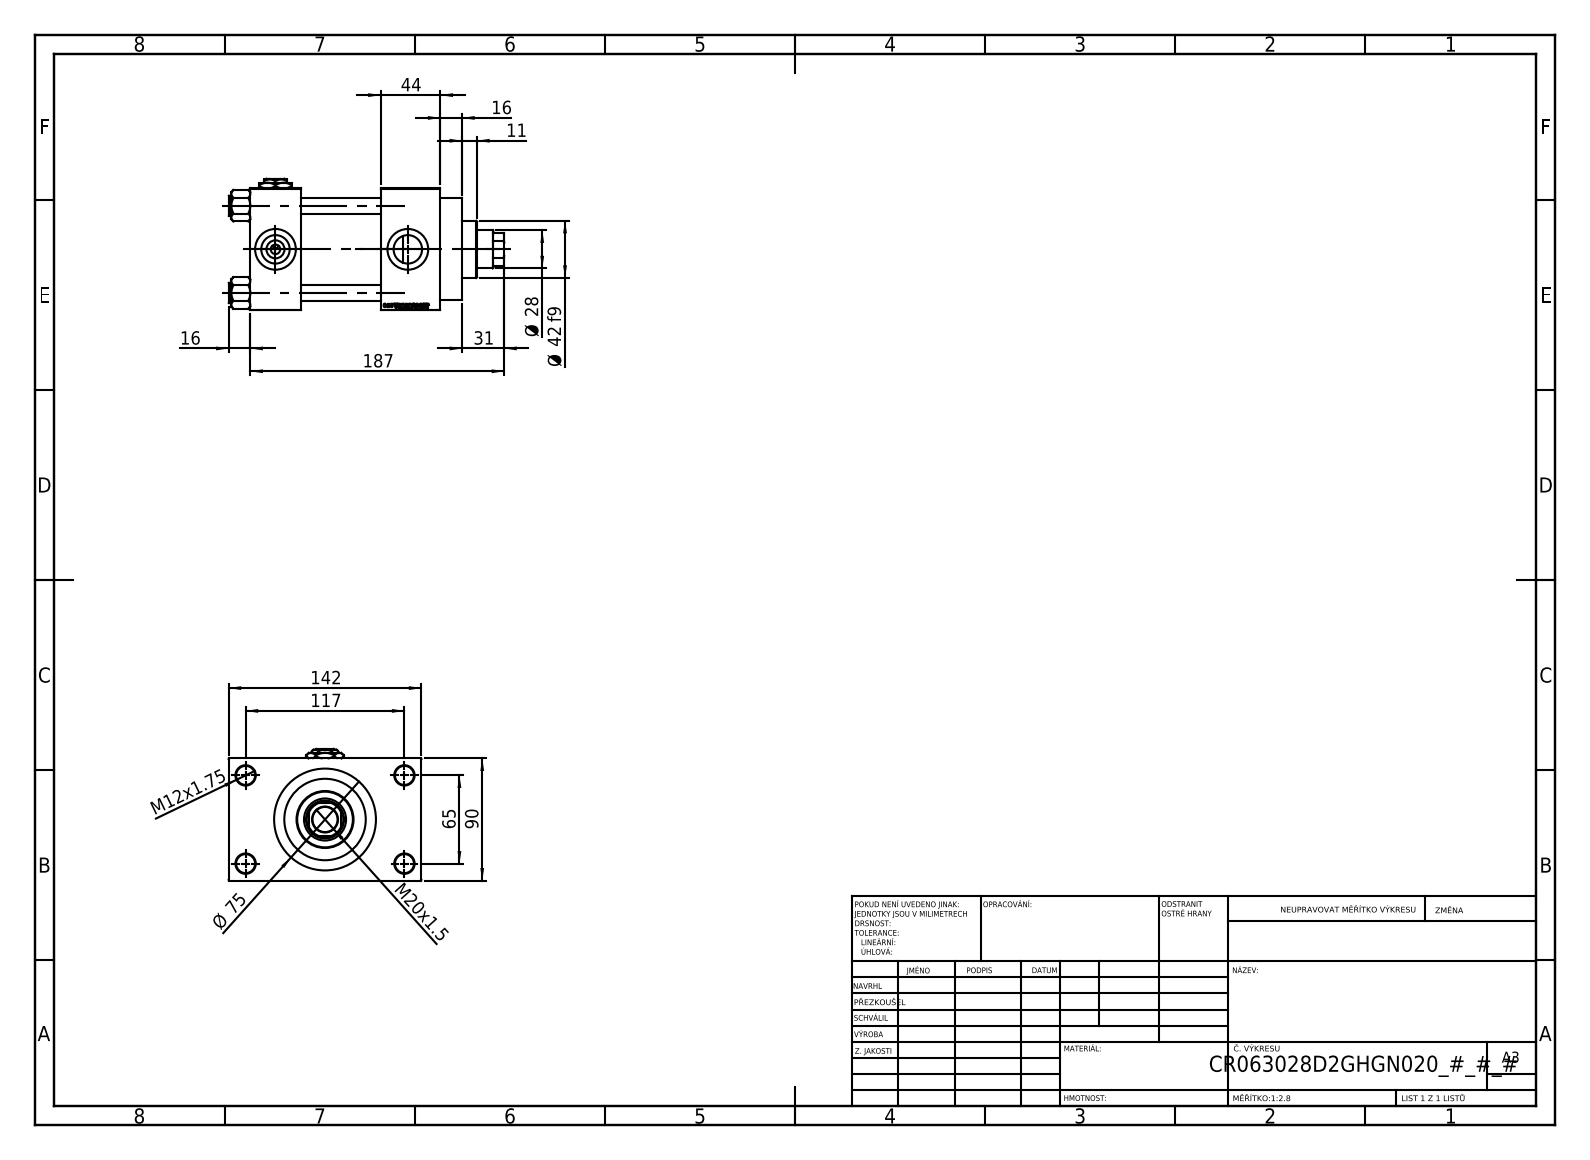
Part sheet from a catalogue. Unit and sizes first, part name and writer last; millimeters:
Units: millimetres
Overall size (bounding box): 203 × 142 × 97
Round holes (diameter × count): ⌀12 ×4, ⌀14 ×4, ⌀7 ×3, ⌀20.96 ×3, ⌀30 ×3, ⌀18.5 ×1, ⌀28 ×1, ⌀31 ×1, ⌀50 ×1, ⌀60 ×1, ⌀63 ×1
Round bosses / shafts (diameter × count): ⌀15 ×4, ⌀75 ×1, ⌀69 ×1, ⌀42 ×1
Partial cylindrical surfaces — rounded edges, fillets, slot ends (radius × count): R13.5 ×1
Main face-to-face distances: 90, 59, 37, 96, 140, 103, 44, 26, 116, 16
Hole centre spacings: 26.35, 45.47, 64.3, 66.92, 69.81, 90.65, 111.34, 65
Volume: 1 094 000 mm³ · Surface area: 203 085 mm²
Bodies: 12 solids, 1156 faces (521 planar, 95 cylindrical, 540 other)
Part name (STEP PRODUCT): V215_VC_A; Zatka_pro_OIL_PORT; V215CR_VCP_D; V215CR_D_Body (+2 more)
STEP written by: SolidWorks 2019 (CONFIG_CONTROL_DESIGN)
